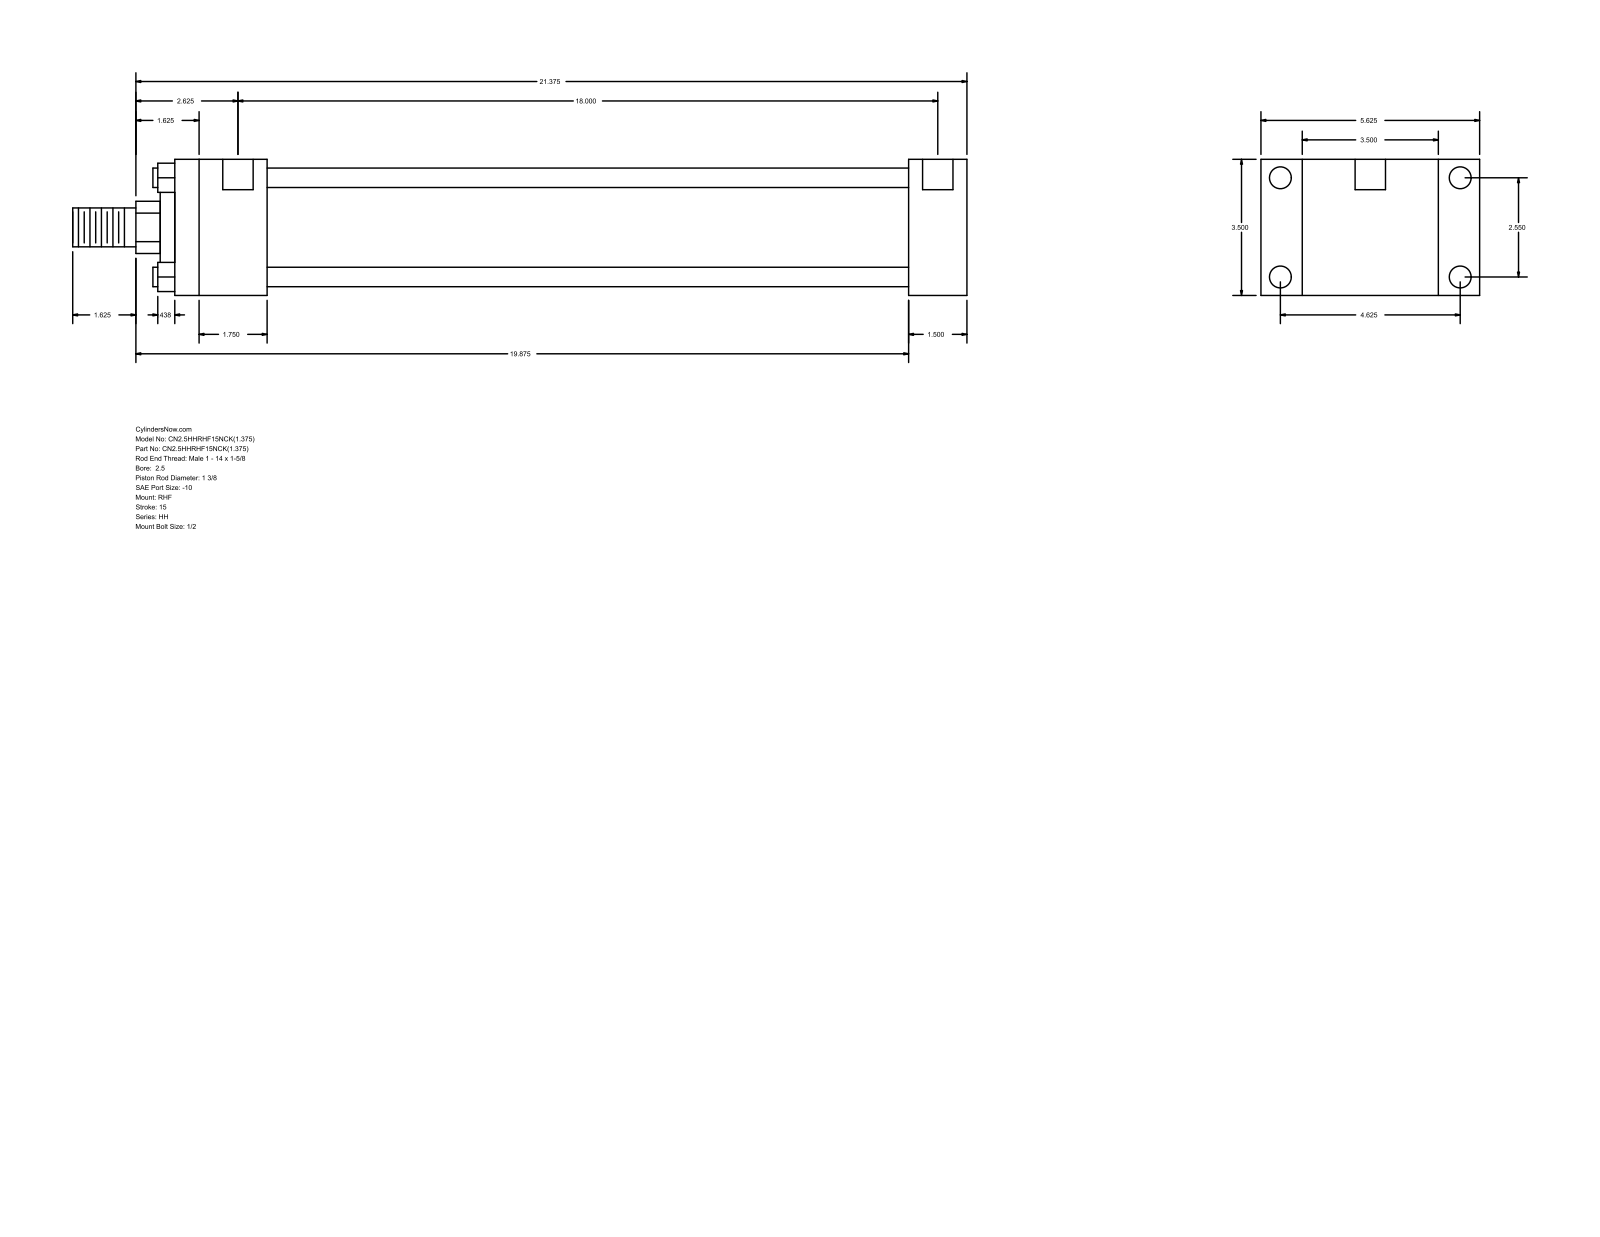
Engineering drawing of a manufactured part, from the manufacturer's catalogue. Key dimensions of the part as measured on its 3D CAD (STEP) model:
Part name (STEP PRODUCT): HH_RHF__0250_1.375
STEP written by: GSSL Pune (CONFIG_CONTROL_DESIGN)
Units: millimetres
Bodies: 0 solids, 88 faces (60 planar, 28 cylindrical, 0 other)
Overall size (bounding box): 584.2 × 142.88 × 88.9
Round holes (diameter × count): ⌀5.56 ×4, ⌀14.3 ×4, ⌀19.84 ×2
Round bosses / shafts (diameter × count): ⌀12.7 ×4, ⌀73.03 ×1, ⌀50.8 ×1, ⌀34.92 ×1, ⌀25.4 ×1
Partial cylindrical surfaces — rounded edges, fillets, slot ends (radius × count): R17.06 ×1
Main face-to-face distances: 88.9, 38.1, 26.99, 115.89, 479.42, 517.52, 142.88, 60.32, 419.1, 457.2
Hole centre spacings: 1.58, 64.76, 117.48, 134.15, 458.79, 460.37, 457.21
